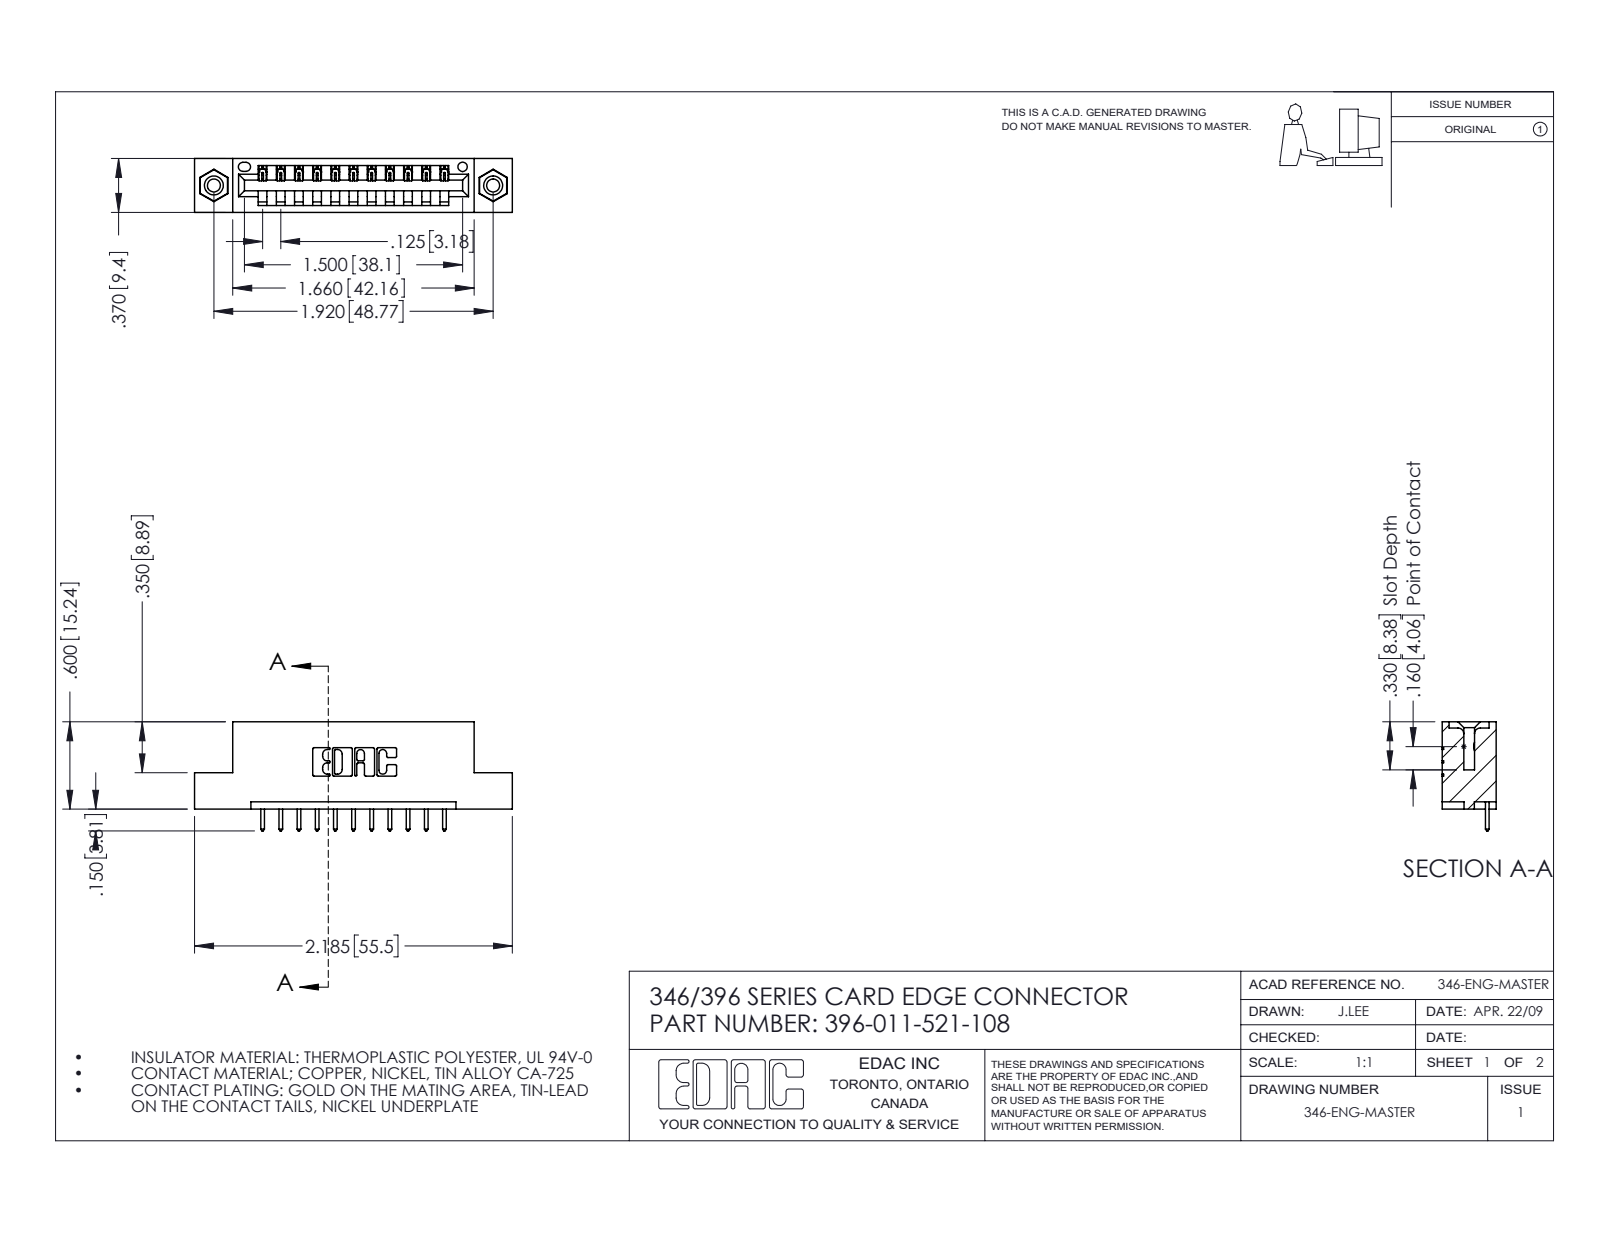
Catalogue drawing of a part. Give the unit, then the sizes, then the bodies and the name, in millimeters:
Units: millimetres
Overall size (bounding box): 55.5 × 19.1 × 9.4
Round holes (diameter × count): ⌀2.3 ×2, ⌀3.2 ×2, ⌀4 ×2, ⌀1.6 ×1
Round bosses / shafts (diameter × count): ⌀3.9 ×2
Partial cylindrical surfaces — rounded edges, fillets, slot ends (radius × count): R0.2 ×22, R0.3 ×22, R0.3 ×22, R0.2 ×6, R0.8 ×6, R0.7 ×3, R0.8 ×2, R1 ×2
Main face-to-face distances: 6.4, 9.4, 1.2, 8.2, 3.8, 5.6, 2.5, 4.4, 1.8, 7.6
Hole centre spacings: 6.2, 43.6, 48.8
Volume: 5 060 mm³ · Surface area: 5 888 mm²
Bodies: 14 solids, 820 faces (548 planar, 256 cylindrical, 16 other)
Part name (STEP PRODUCT): 346 Part_Flush Mounting Lugs - 0.156 Dia-TI; 345-292-001_345-293-121; 345-250-001_345-250-003-102; 396-011-521-108
STEP written by: SolidWorks 2016 (CONFIG_CONTROL_DESIGN)
